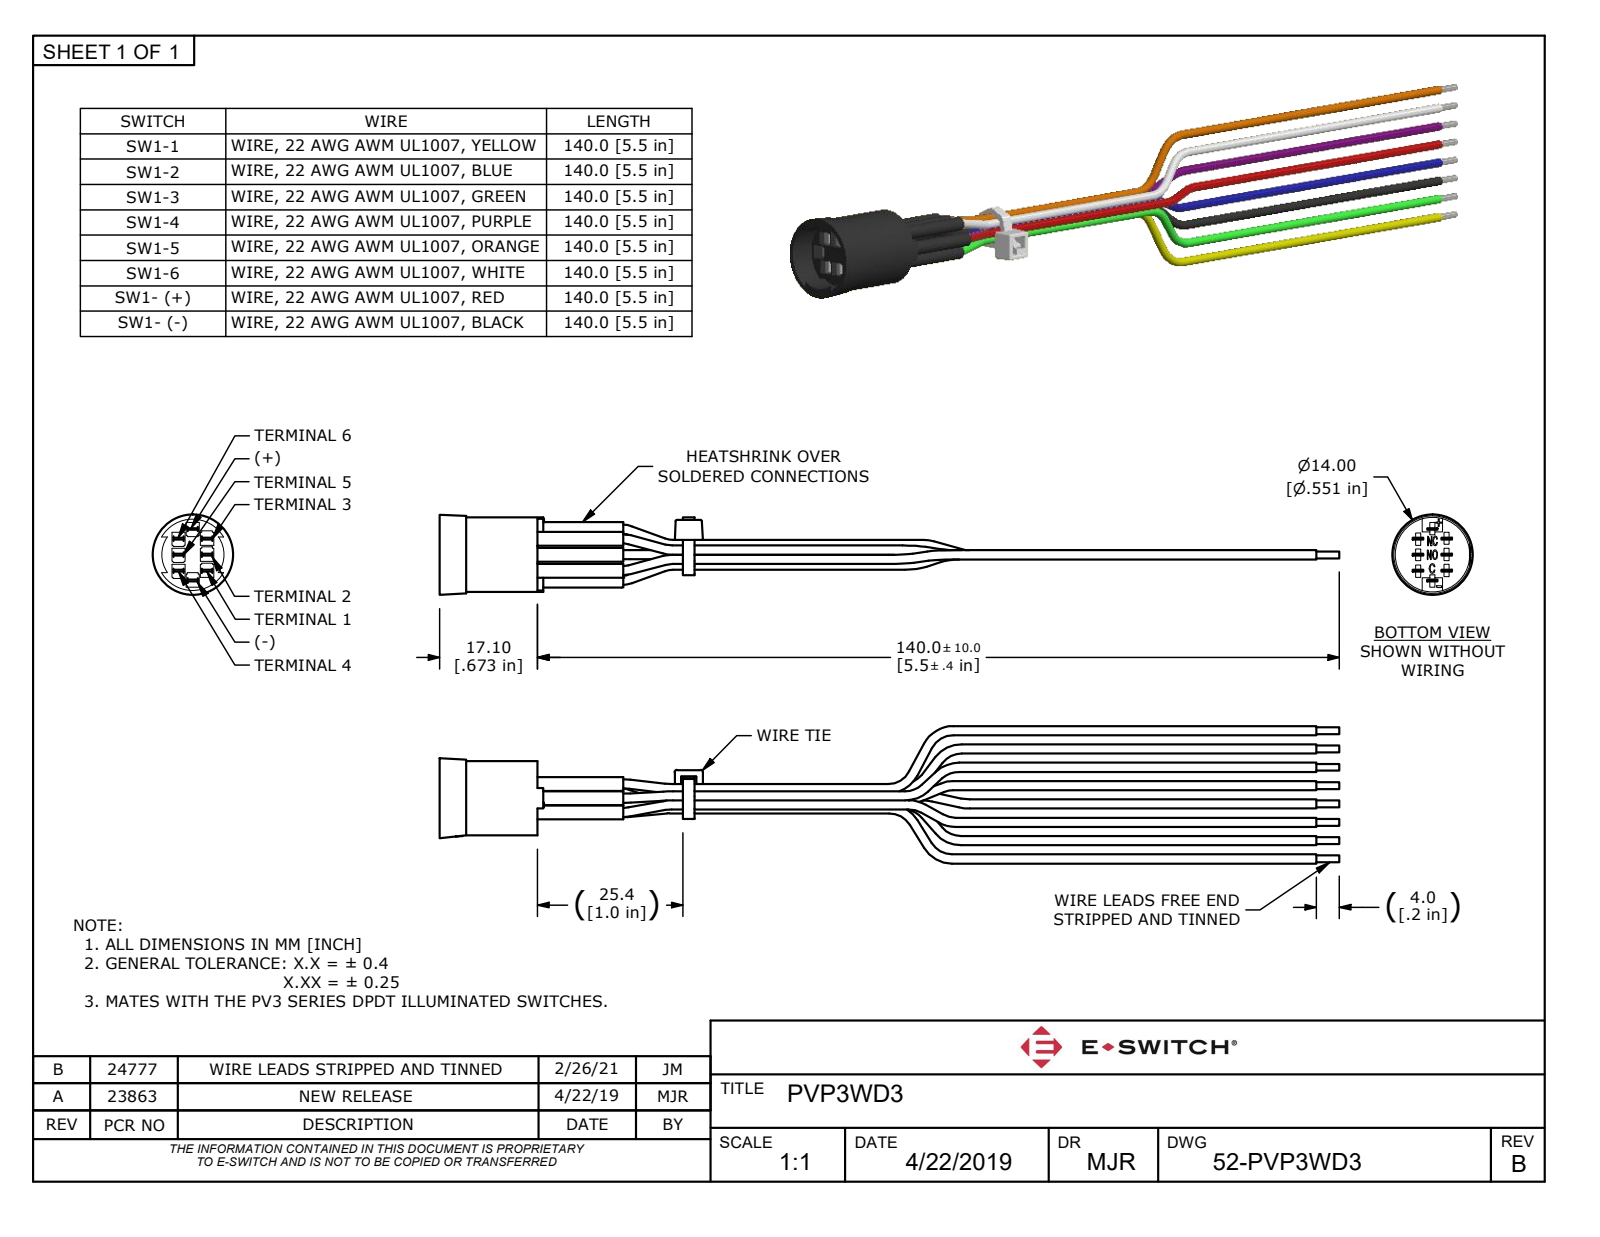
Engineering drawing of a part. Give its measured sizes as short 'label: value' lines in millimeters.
name: PVP3WD3
written by: Autodesk Inventor 2018 (AP242_MANAGED_MODEL_BASED_3D_ENGINEERING_MIM_LF)
unit: mm
bodies: 1 solid, 668 faces (415 planar, 136 cylindrical, 117 other)
size: 157.1 × 24 × 14
volume: 4 313 mm³; area: 8 470 mm²
holes: 8× ⌀1.6
bosses: 32× ⌀1.6, 16× ⌀1.2, 8× ⌀2.4, 1× ⌀13
rounds: 18× R0.25, 14× R0.2, 5× R1.1, 3× R0.9, 2× R6.25, 1× R5.4
face distances: 2.8, 2.5, 1.7, 7.3, 5.6, 0.9, 4.5, 3.1, 12.5, 2
hole spacings: 2.8, 3.02, 5.15, 5.73, 7.72, 5, 5.6, 7.51
